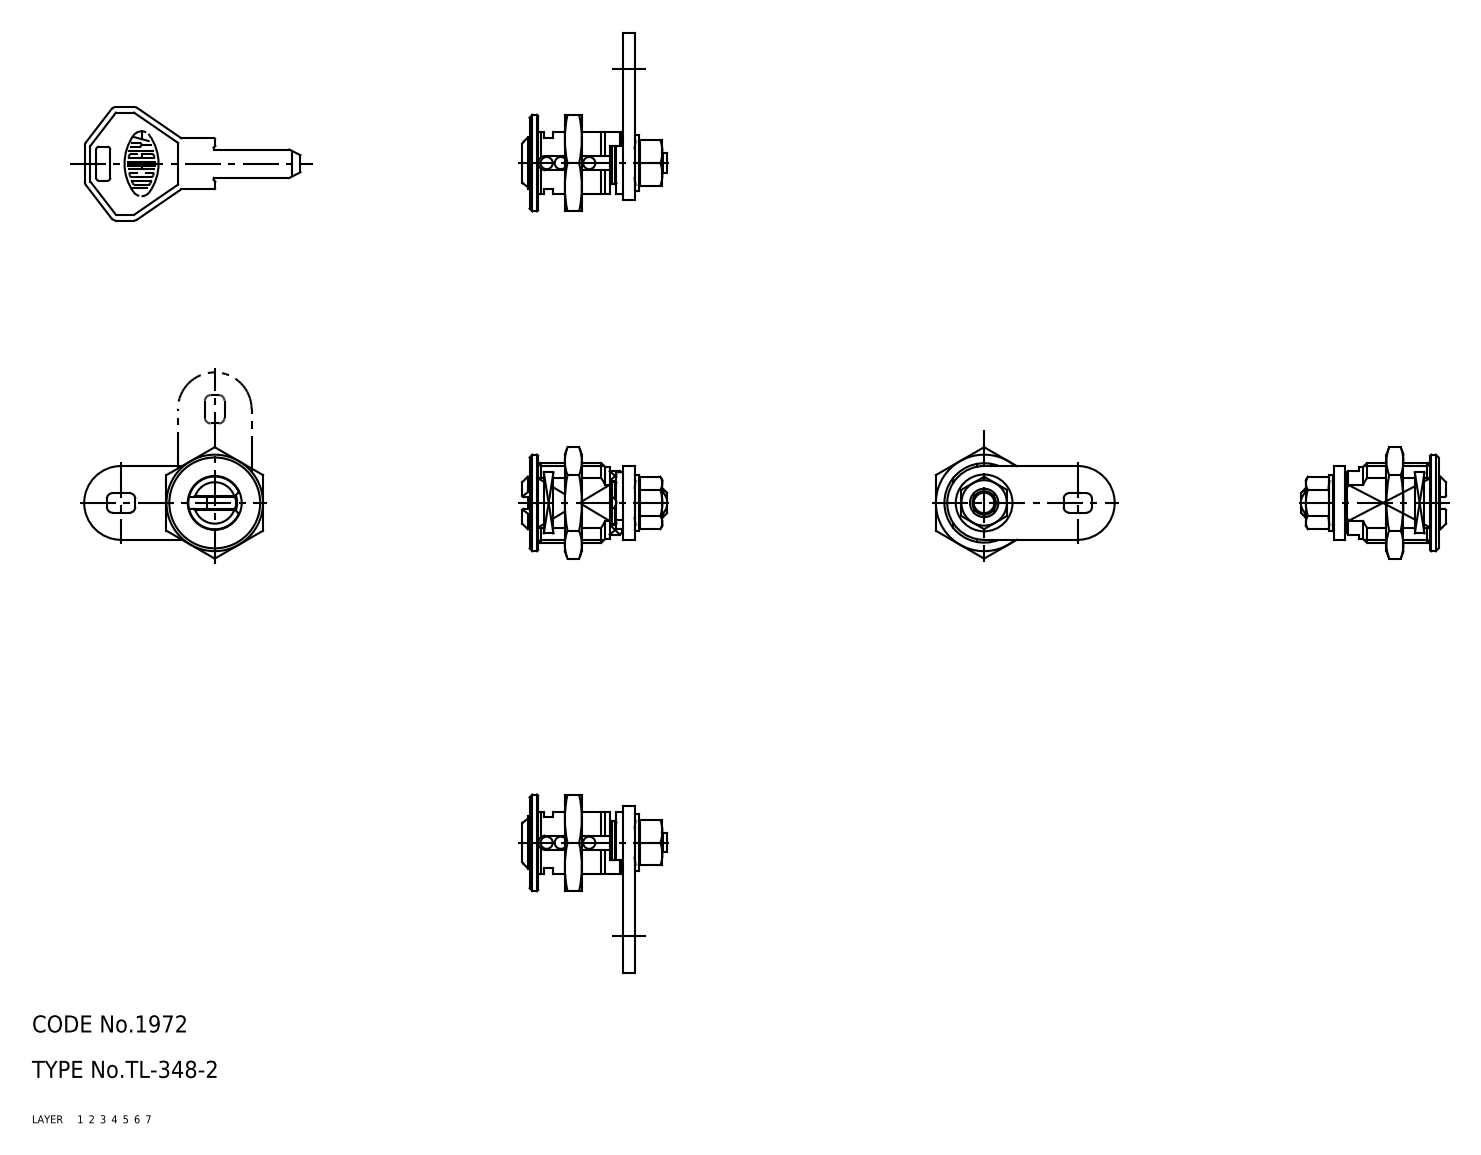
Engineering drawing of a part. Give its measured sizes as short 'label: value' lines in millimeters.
name: nut_B; washer; nut_A; lock (+4 more)
written by: CADfix (AUTOMOTIVE_DESIGN)
unit: mm
bodies: 7 solids, 202 faces (0 planar, 0 cylindrical, 202 other)
size: 87.57 × 33.12 × 19.63
volume: 3 944 mm³; area: 4 446 mm²
